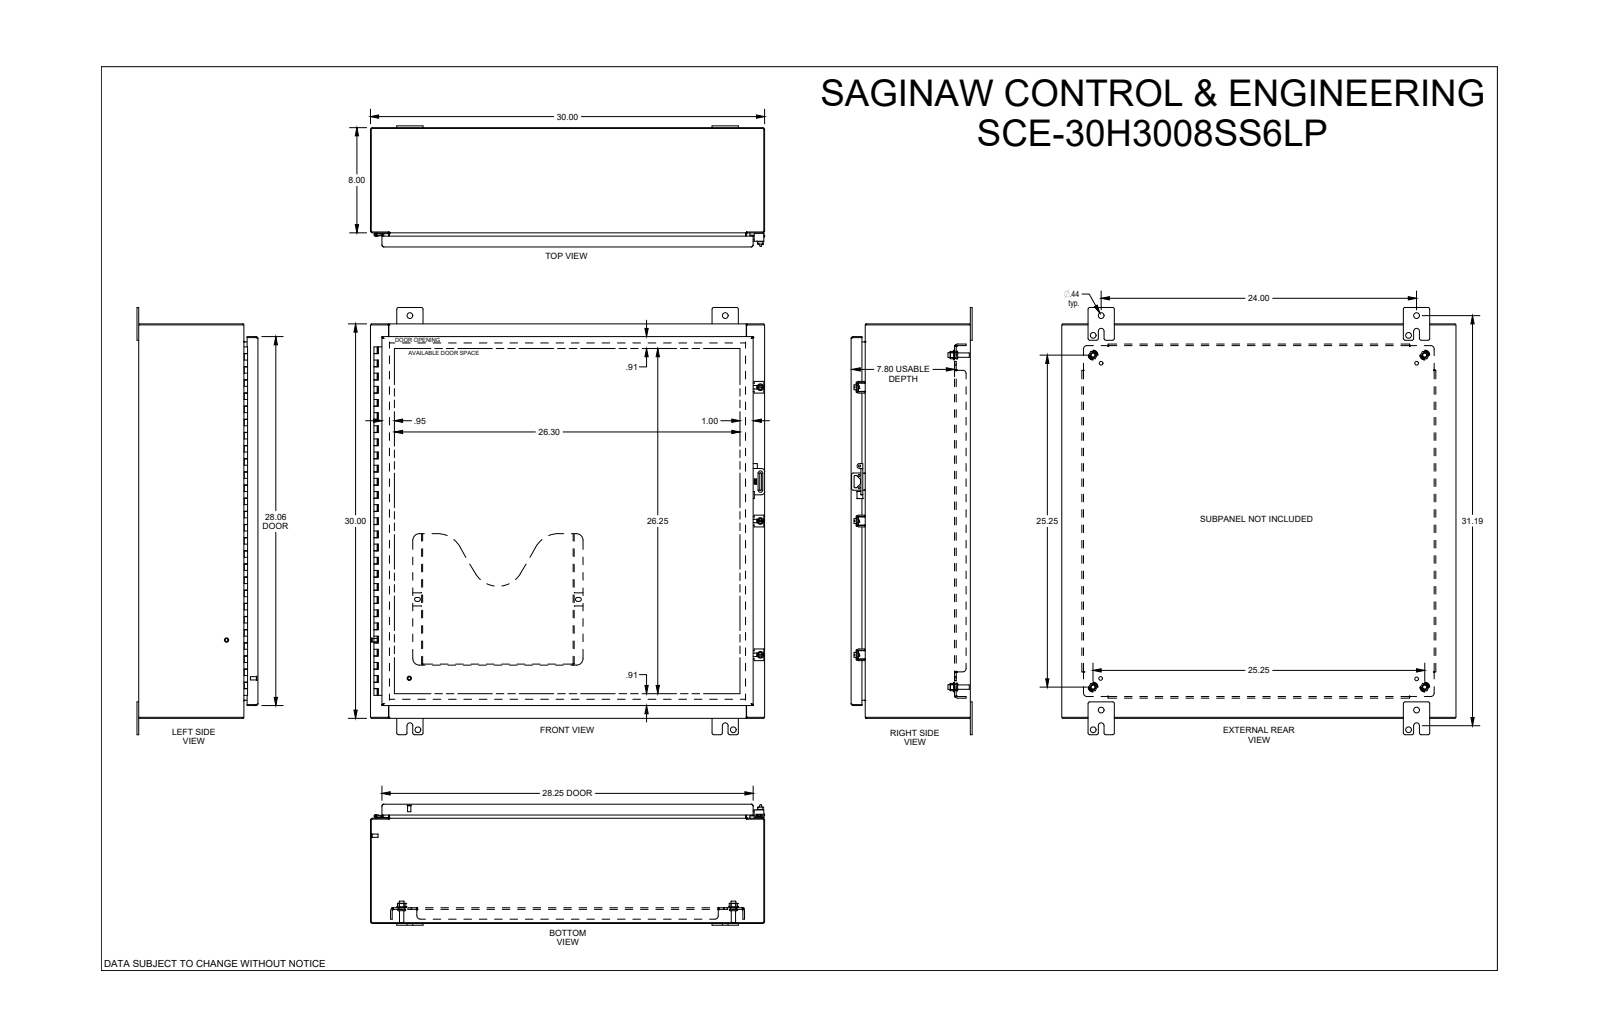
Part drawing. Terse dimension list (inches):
name: SCE-30H3008SS6LP
written by: SolidWorks 2019 (CONFIG_CONTROL_DESIGN)
unit: in
bodies: 0 solids, 3825 faces (1563 planar, 800 cylindrical, 1462 other)
size: 32.5 × 30 × 9.208
holes: 8× ⌀0.437, 6× ⌀0.25, 5× ⌀0.19, 5× ⌀0.193, 4× ⌀0.281, 4× ⌀0.367, 4× ⌀0.5, 3× ⌀0.203, 2× ⌀0.16, 1× ⌀0.13, 1× ⌀0.132
bosses: 8× ⌀0.248, 6× ⌀0.563, 5× ⌀0.256, 5× ⌀0.188, 4× ⌀0.366, 4× ⌀0.332, 4× ⌀0.25, 3× ⌀0.507
rounds: 148× R0.01, 40× R0.015, 36× R0.029, 29× R0.06, 27× R0.03, 27× R0.125, 22× R0.04, 14× R0.07
face distances: 0.075, 29.925, 8.998, 8.923, 0.075, 1.2, 7.873, 9.073, 8.998, 7.923
hole spacings: 24.639, 24, 0.515, 0.875, 6.375, 6.375, 12.75, 27.007
